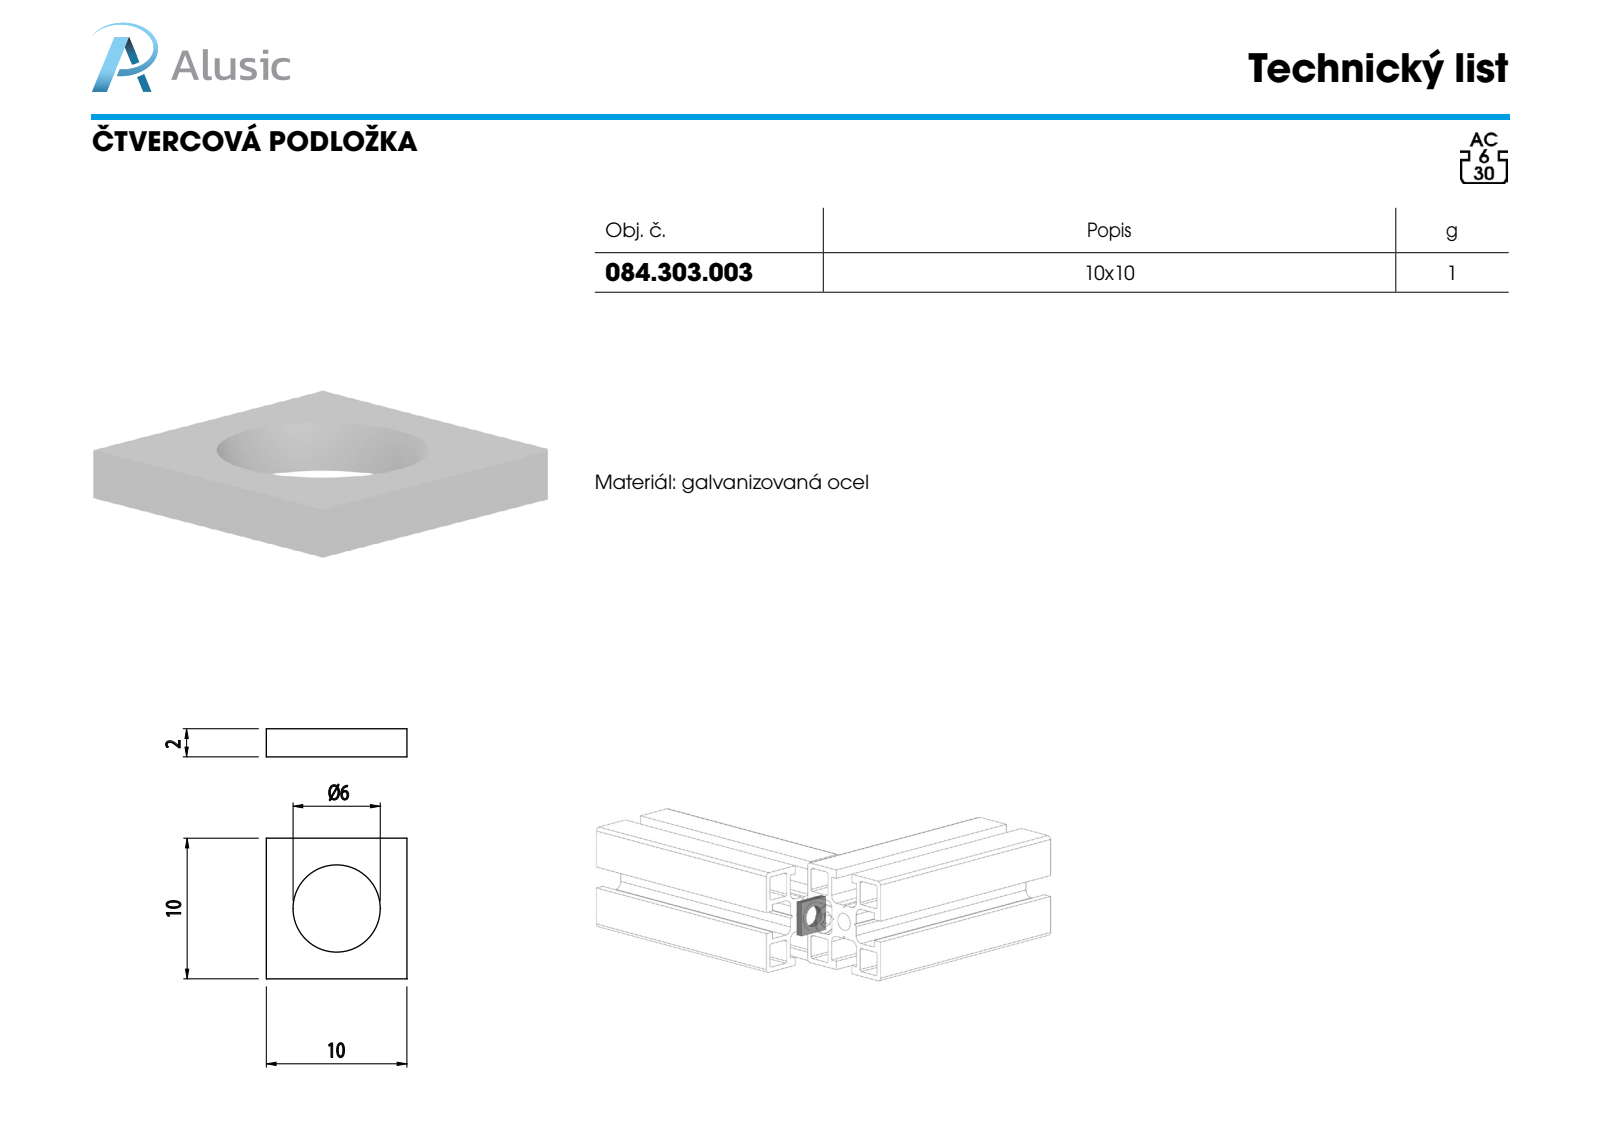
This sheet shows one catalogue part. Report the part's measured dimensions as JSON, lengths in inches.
{"part_name": "084.303.003", "step_written_by": "SolidWorks 2011 (CONFIG_CONTROL_DESIGN)", "units": "inches", "bodies": {"solids": 1, "faces": 8, "planar": 6, "cylindrical": 2, "other": 0}, "overall_size": [0.394, 0.394, 0.079], "volume_in3": 0.009, "surface_area_in2": 0.401, "round_holes": [[0.244, 1]], "face_to_face_distances": [0.079, 0.394]}
